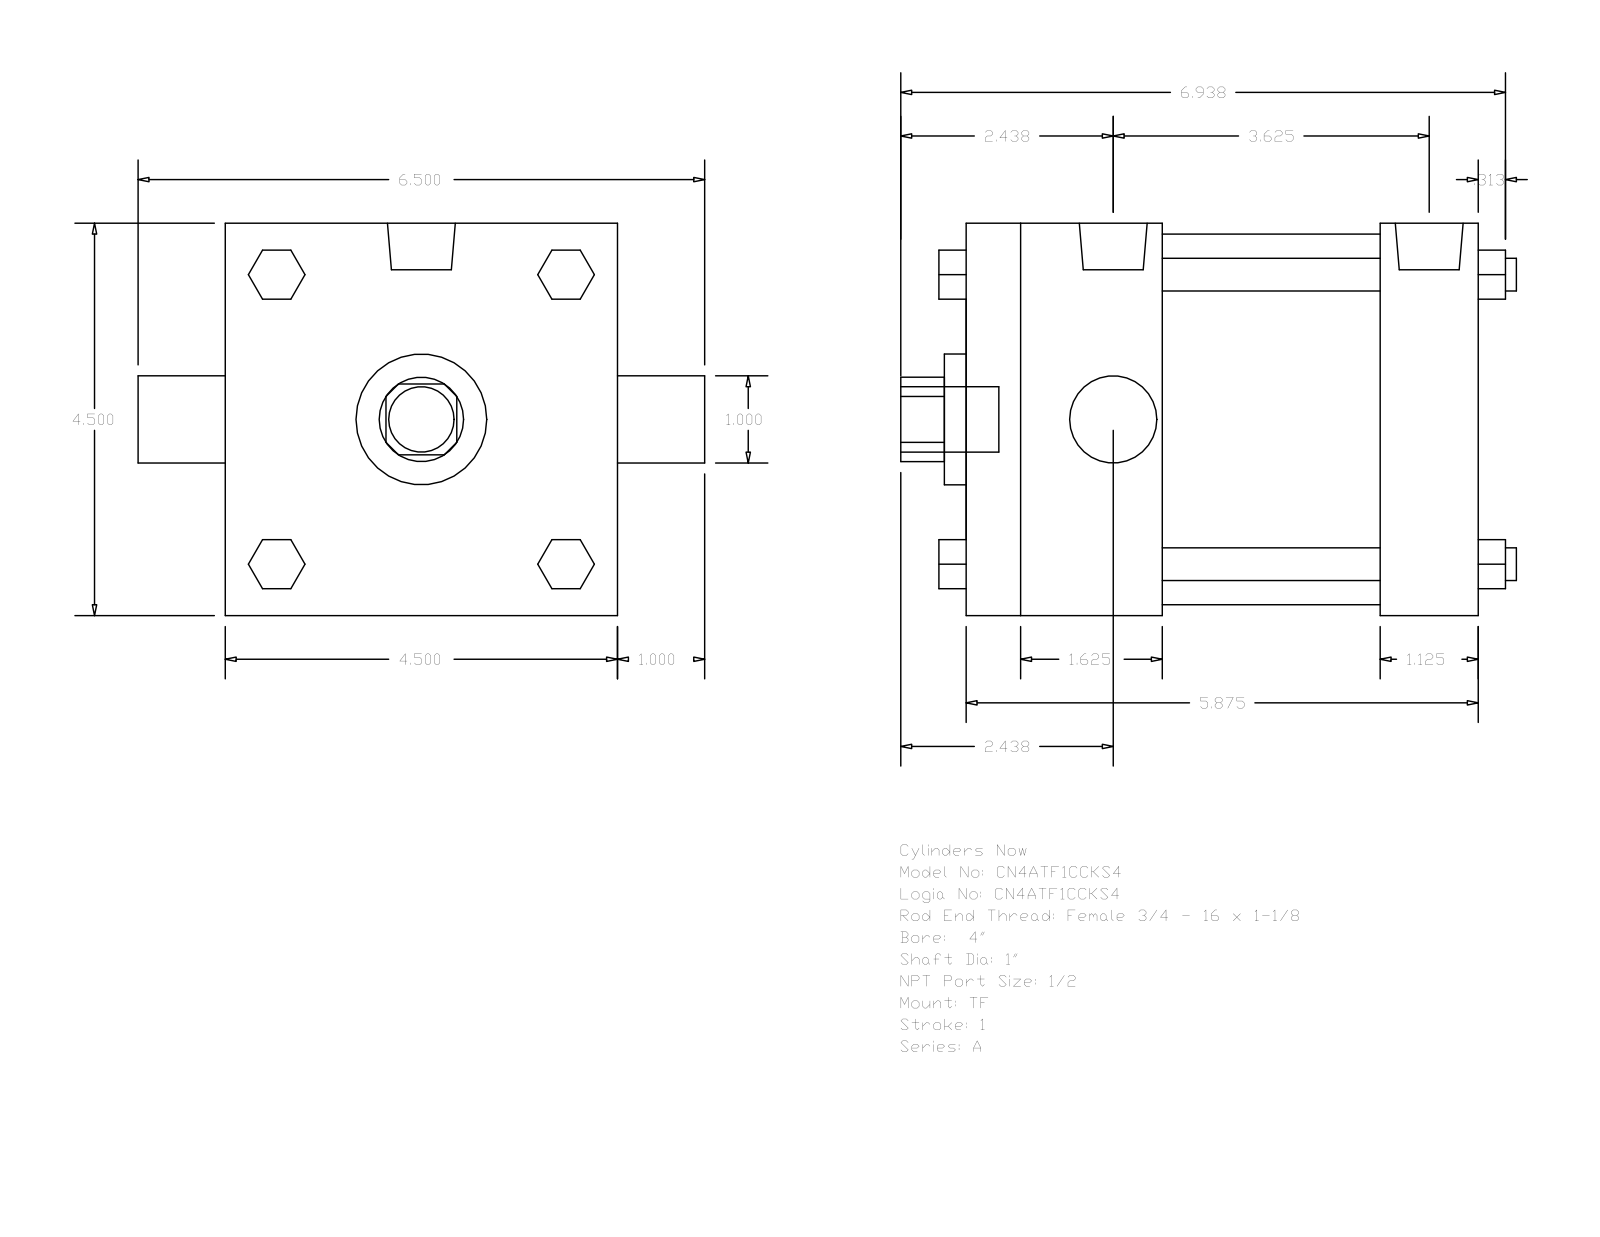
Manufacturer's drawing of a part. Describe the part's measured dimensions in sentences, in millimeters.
The part is named "A_TF__0400_1". Its 3-D file was written by "GSSL Pune (CONFIG_CONTROL_DESIGN)". It is 0 solids with 120 faces: 92 planar, 28 cylindrical and 0 other. Overall it measures 179.39 by 165.1 by 114.3 millimeters. Round holes: 2 of diameter 25.4, 1 of diameter 38.1, 1 of diameter 107.95. Round bosses or shafts: 4 of diameter 9.53, 3 of diameter 8.73, 2 of diameter 19.77, 1 of diameter 19.05. Partial cylindrical surfaces (rounded edges, fillets, slot ends): 1 of radius 12.29. The main face-to-face distances are 114.3, 149.23, 63.5, 120.65, 28.58, 57.15, 92.08, 14.29, 139.7, 42.16.
